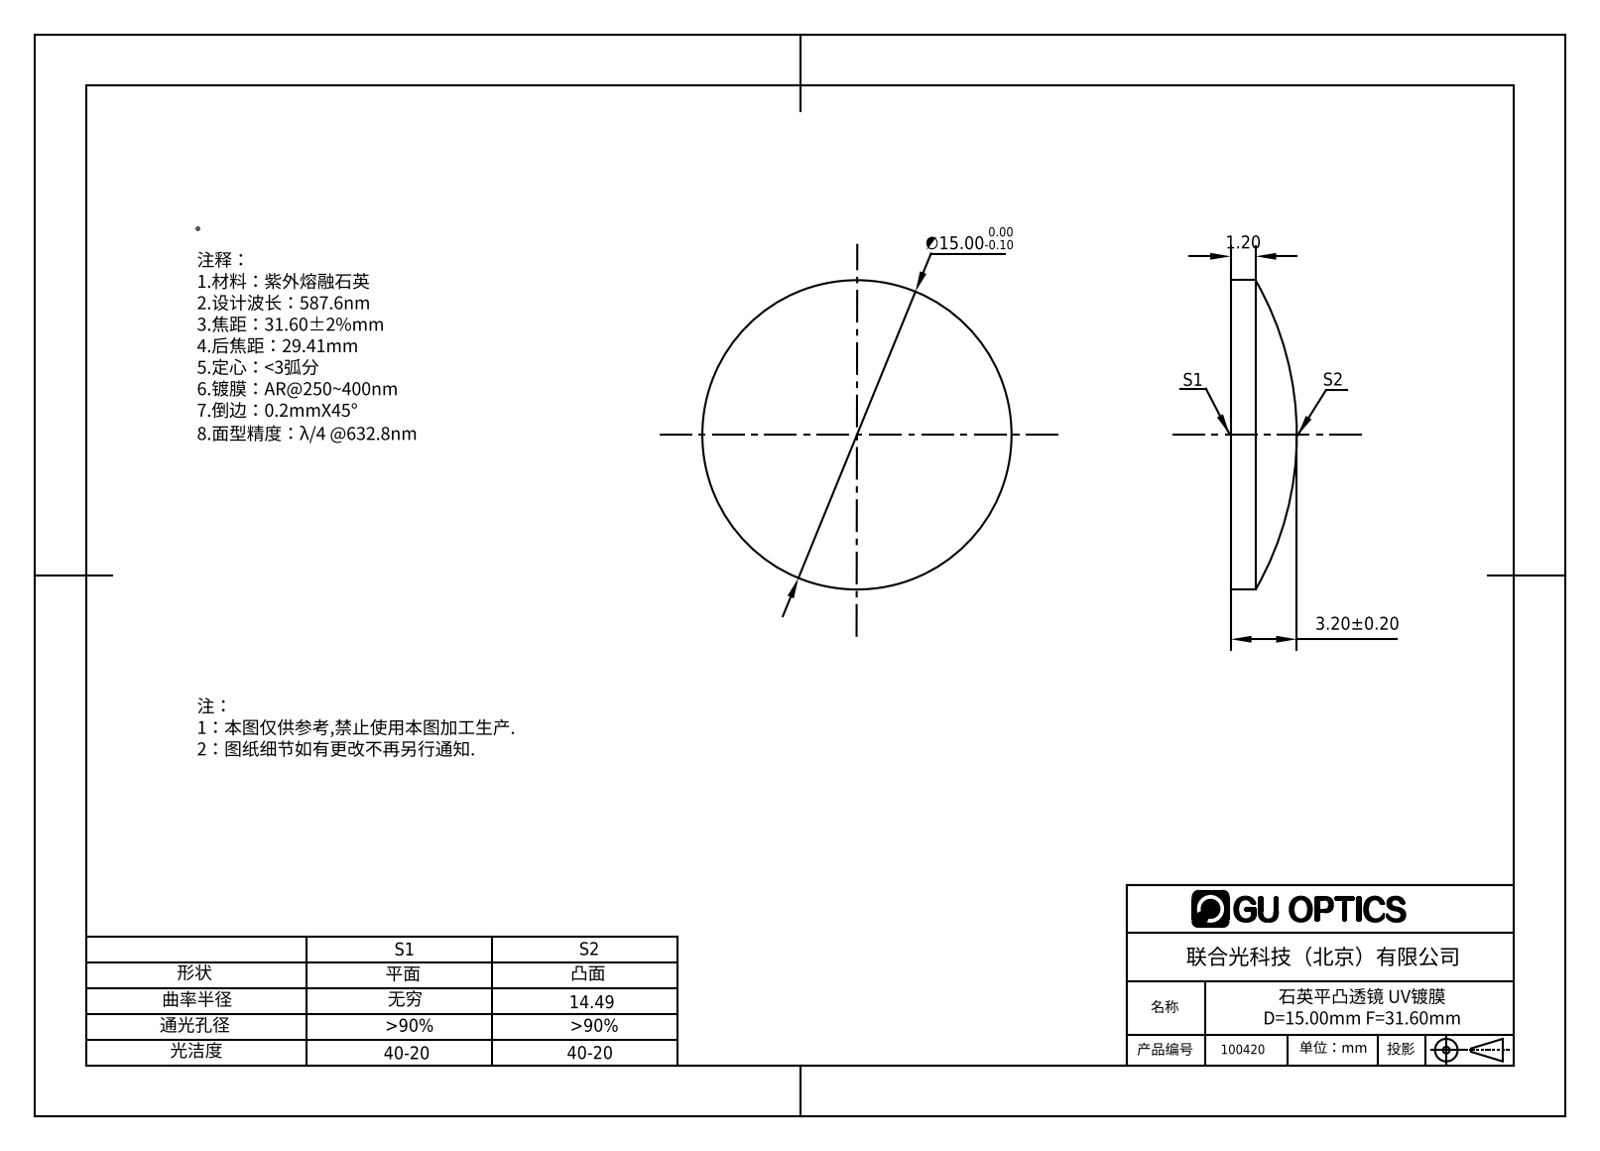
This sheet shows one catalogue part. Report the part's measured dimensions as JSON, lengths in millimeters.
{"part_name": "100370", "step_written_by": "SolidWorks 2016 (AUTOMOTIVE_DESIGN)", "units": "millimeters", "bodies": {"solids": 1, "faces": 5, "planar": 1, "cylindrical": 2, "other": 2}, "overall_size": [15, 15, 3.2], "volume_mm3": 393, "surface_area_mm2": 423, "round_bosses_or_shafts": [[15, 1]]}
